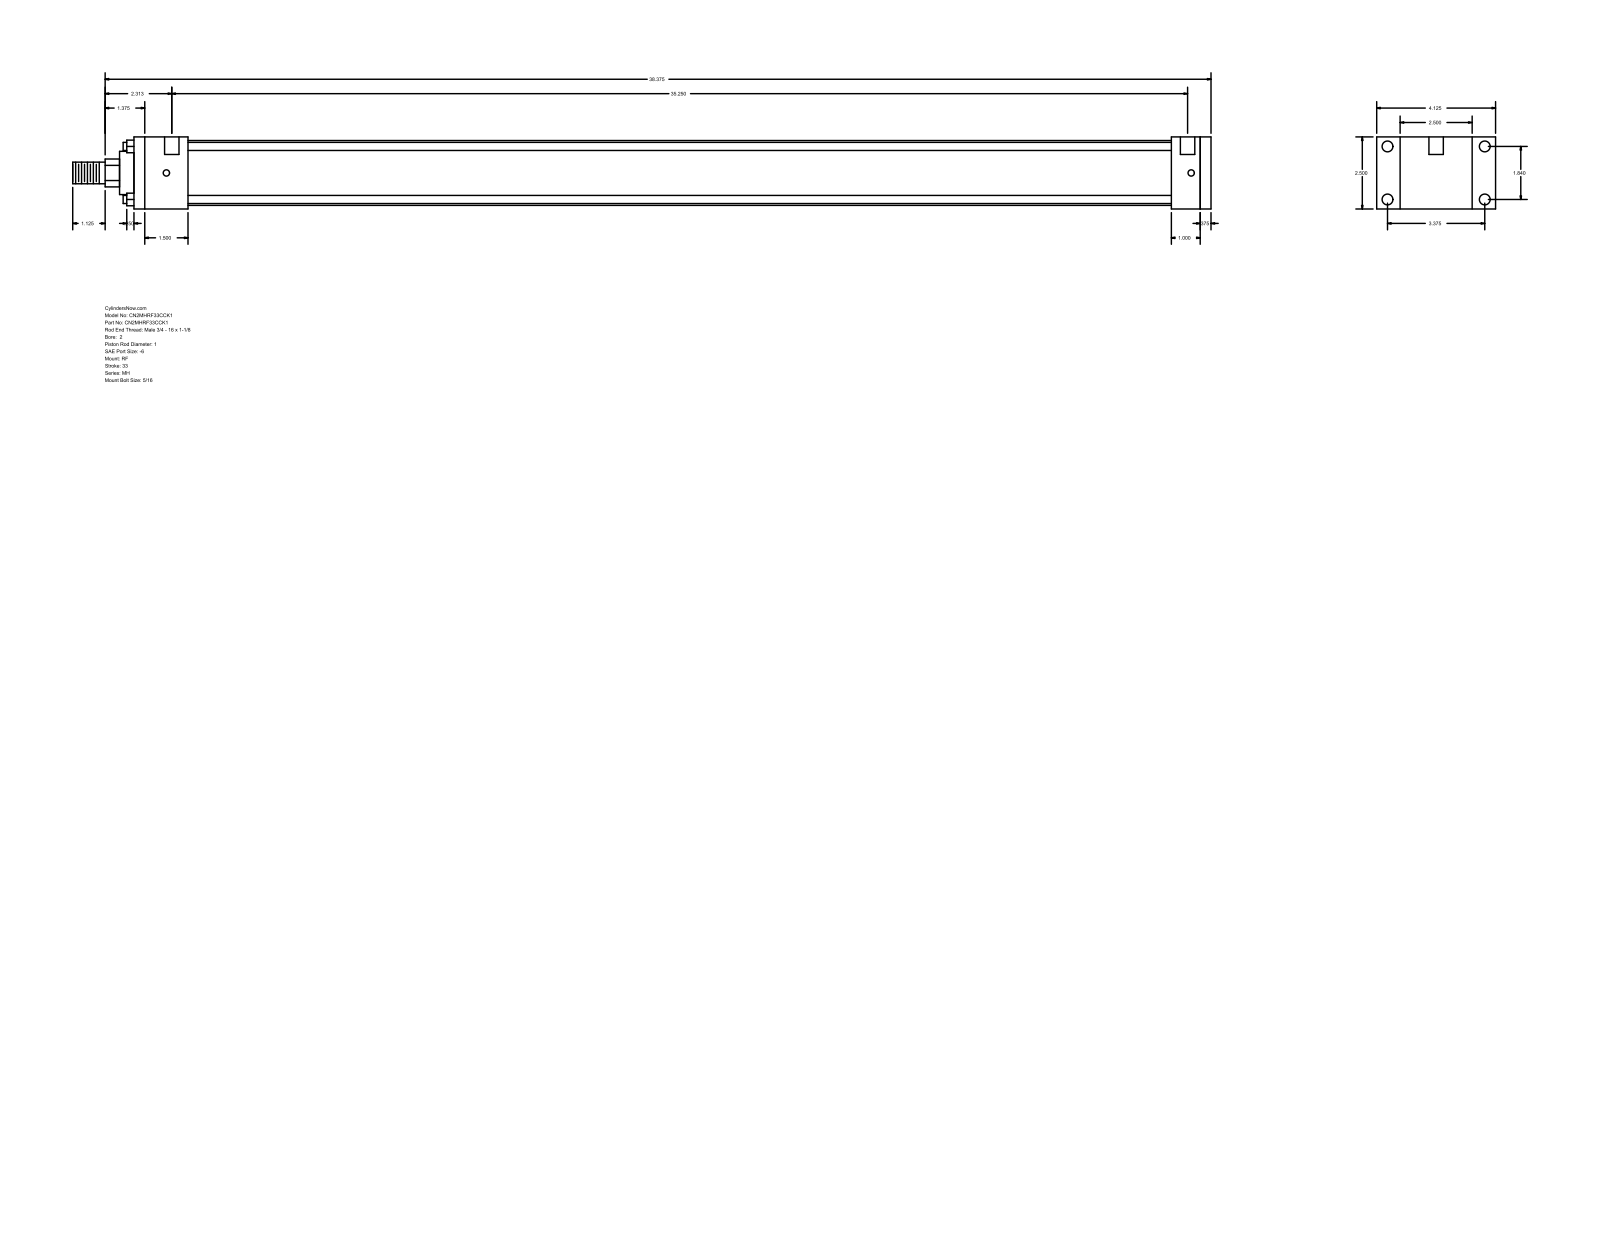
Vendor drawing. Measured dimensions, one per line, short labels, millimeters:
name: MH_RF__0200_1
written by: GSSL Pune (CONFIG_CONTROL_DESIGN)
unit: mm
bodies: 0 solids, 92 faces (64 planar, 28 cylindrical, 0 other)
size: 1003.3 × 104.78 × 63.5
holes: 4× ⌀5.56, 4× ⌀9.53, 2× ⌀12.7
bosses: 4× ⌀7.14, 1× ⌀57.15, 1× ⌀38.1, 1× ⌀25.4, 1× ⌀19.05
rounds: 1× R12.29
face distances: 63.5, 949.33, 939.8, 9.53, 20.64, 25.4, 47.63, 914.4, 866.77, 892.17
hole spacings: 46.74, 85.72, 97.63, 903.28, 3.17, 4.76, 895.35, 898.52
